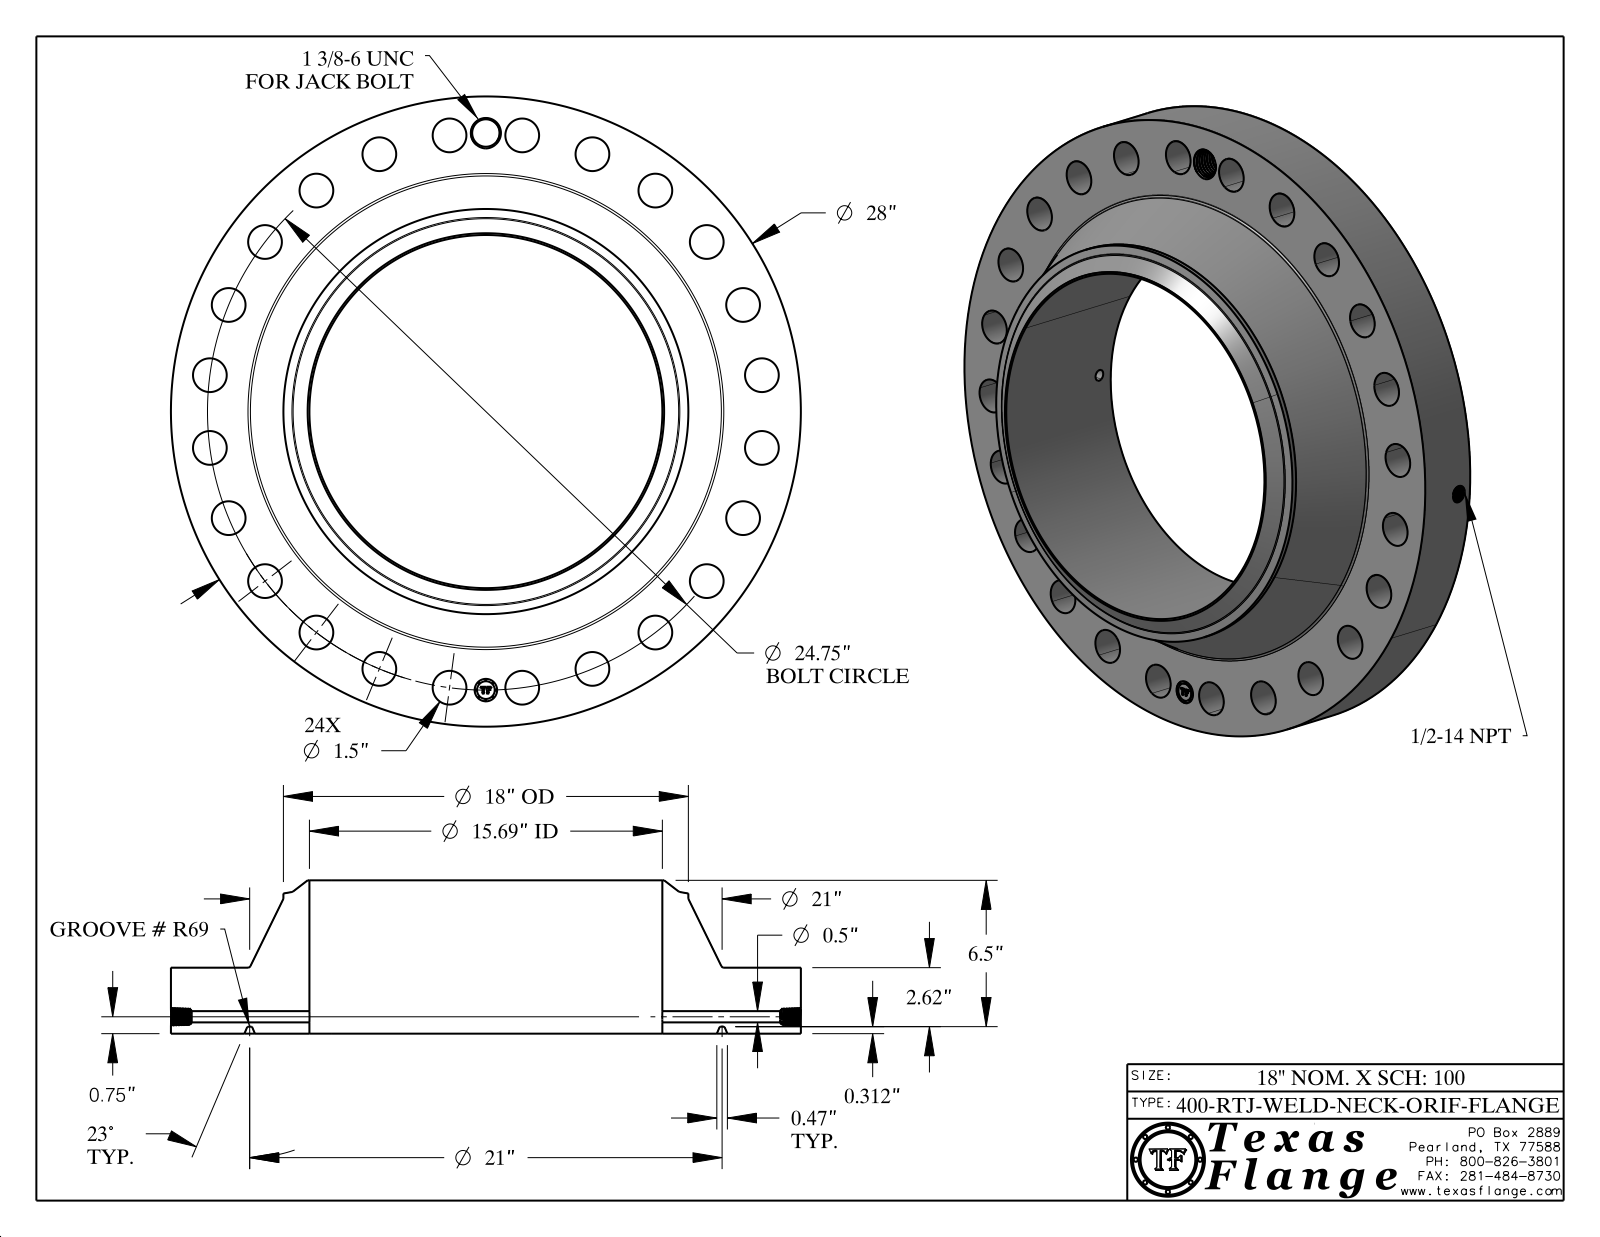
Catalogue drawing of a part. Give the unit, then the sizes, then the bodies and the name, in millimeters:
Units: millimetres
Overall size (bounding box): 711.2 × 711.2 × 173
Round holes (diameter × count): ⌀38.1 ×24, ⌀12.7 ×1, ⌀17.1 ×1, ⌀25.4 ×1, ⌀31 ×1, ⌀398.5 ×1
Round bosses / shafts (diameter × count): ⌀1.5 ×8, ⌀711.2 ×1, ⌀457.2 ×1, ⌀20 ×1
Main face-to-face distances: 74.5, 7.9, 66.5, 173, 165.1, 98.6, 0.4, 74.1, 66.2, 98.9
Hole centre spacings: 314.3, 382.7, 544.4, 580.8, 607.2, 162.7, 444.5, 82
Volume: 23 830 000 mm³ · Surface area: 1 217 000 mm²
Bodies: 1 solid, 828 faces (370 planar, 129 cylindrical, 329 other)
Part name (STEP PRODUCT): 400-RTJ-WELD-NECK
STEP written by: CATIA V5 STEP AP214 (AUTOMOTIVE_DESIGN)
